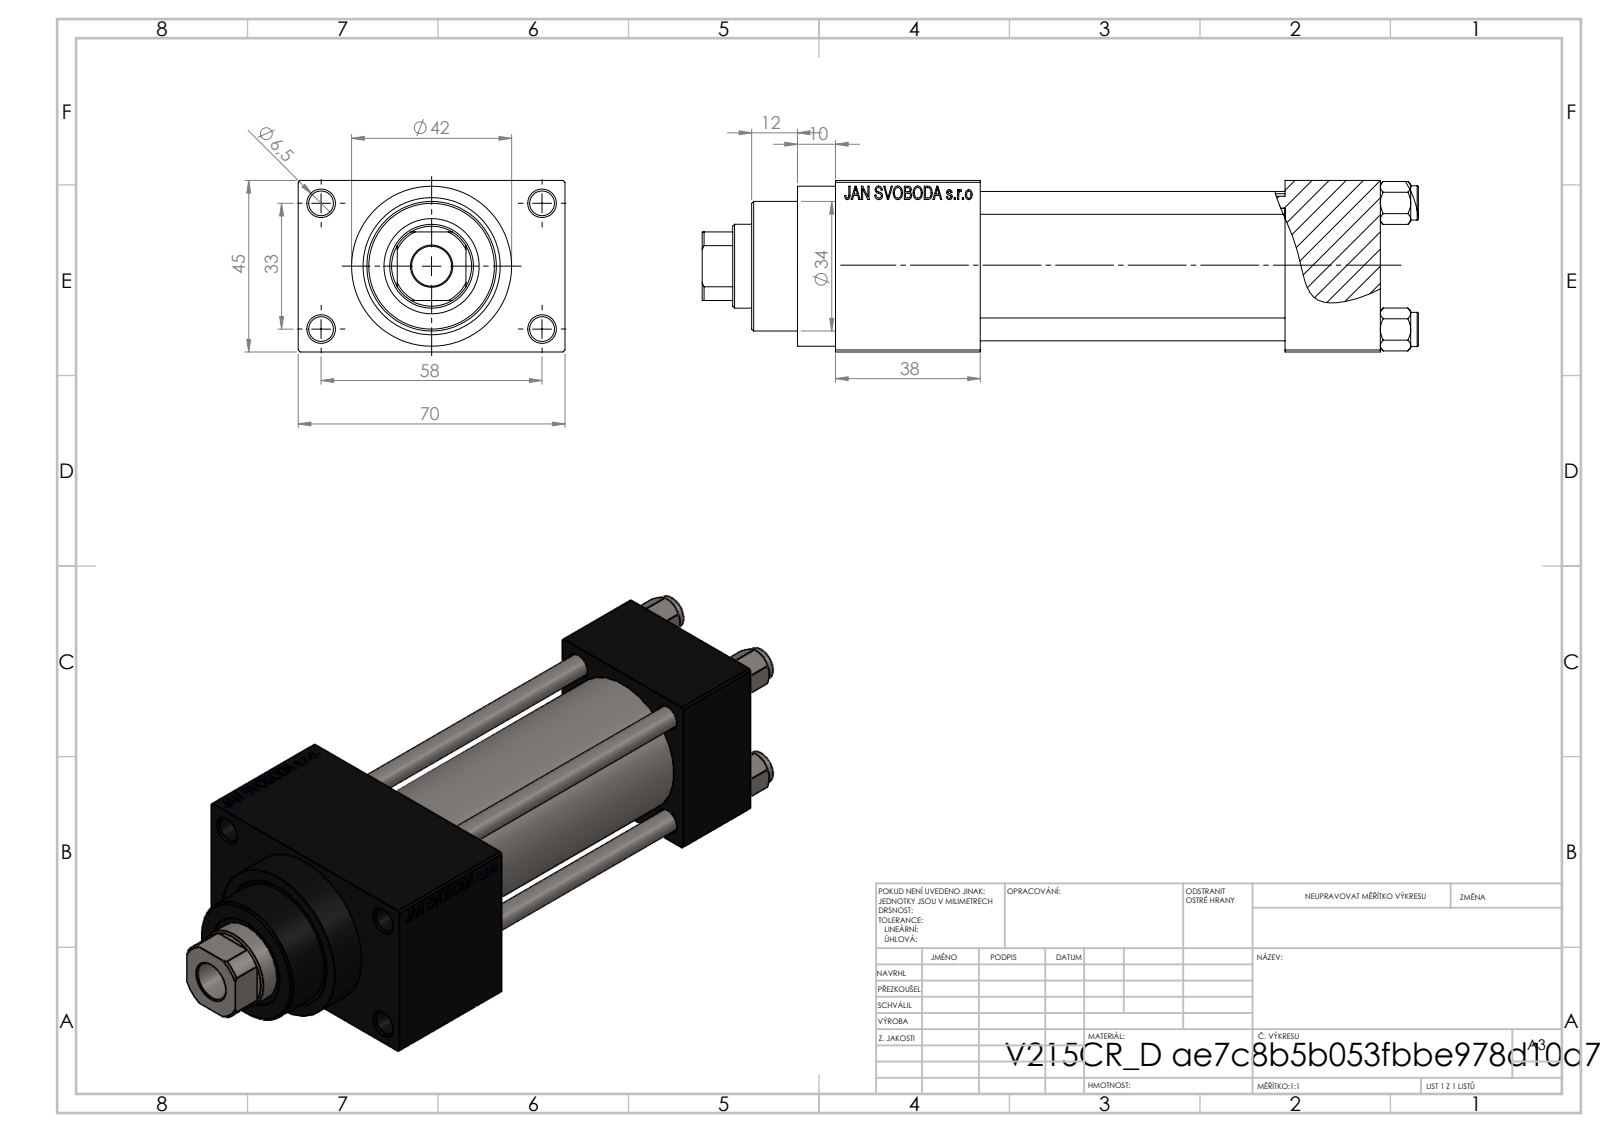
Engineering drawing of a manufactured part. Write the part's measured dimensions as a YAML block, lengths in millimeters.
part_name: "V215_VC_A; NUT_M5_D; V215CR_VCP_D; V215CR_D_TYCINKA (+1 more)"
step_written_by: "SolidWorks 2019 (CONFIG_CONTROL_DESIGN)"
units: millimeters
bodies: {solids: 11, faces: 1104, planar: 496, cylindrical: 88, other: 520}
overall_size: [188, 70, 45]
volume: 267569
surface_area: 90817
round_holes:
  - {diameter: 6, count: 4}
  - {diameter: 6.5, count: 4}
  - {diameter: 7, count: 2}
  - {diameter: 13.16, count: 2}
  - {diameter: 20, count: 2}
  - {diameter: 10.5, count: 1}
  - {diameter: 22, count: 1}
  - {diameter: 24, count: 1}
  - {diameter: 25, count: 1}
  - {diameter: 32, count: 1}
  - {diameter: 33, count: 1}
round_bosses_or_shafts:
  - {diameter: 9, count: 4}
  - {diameter: 42, count: 1}
  - {diameter: 38, count: 1}
  - {diameter: 34, count: 1}
partial_cylinders:
  - {radius: 10.5, count: 1}
face_to_face_distances: [45, 25, 12.5, 80, 105, 57.5, 118, 38, 143, 70]
hole_center_spacings: [12.4, 23.48, 33.2, 33.37, 35.35, 45.6, 56.35, 33]
